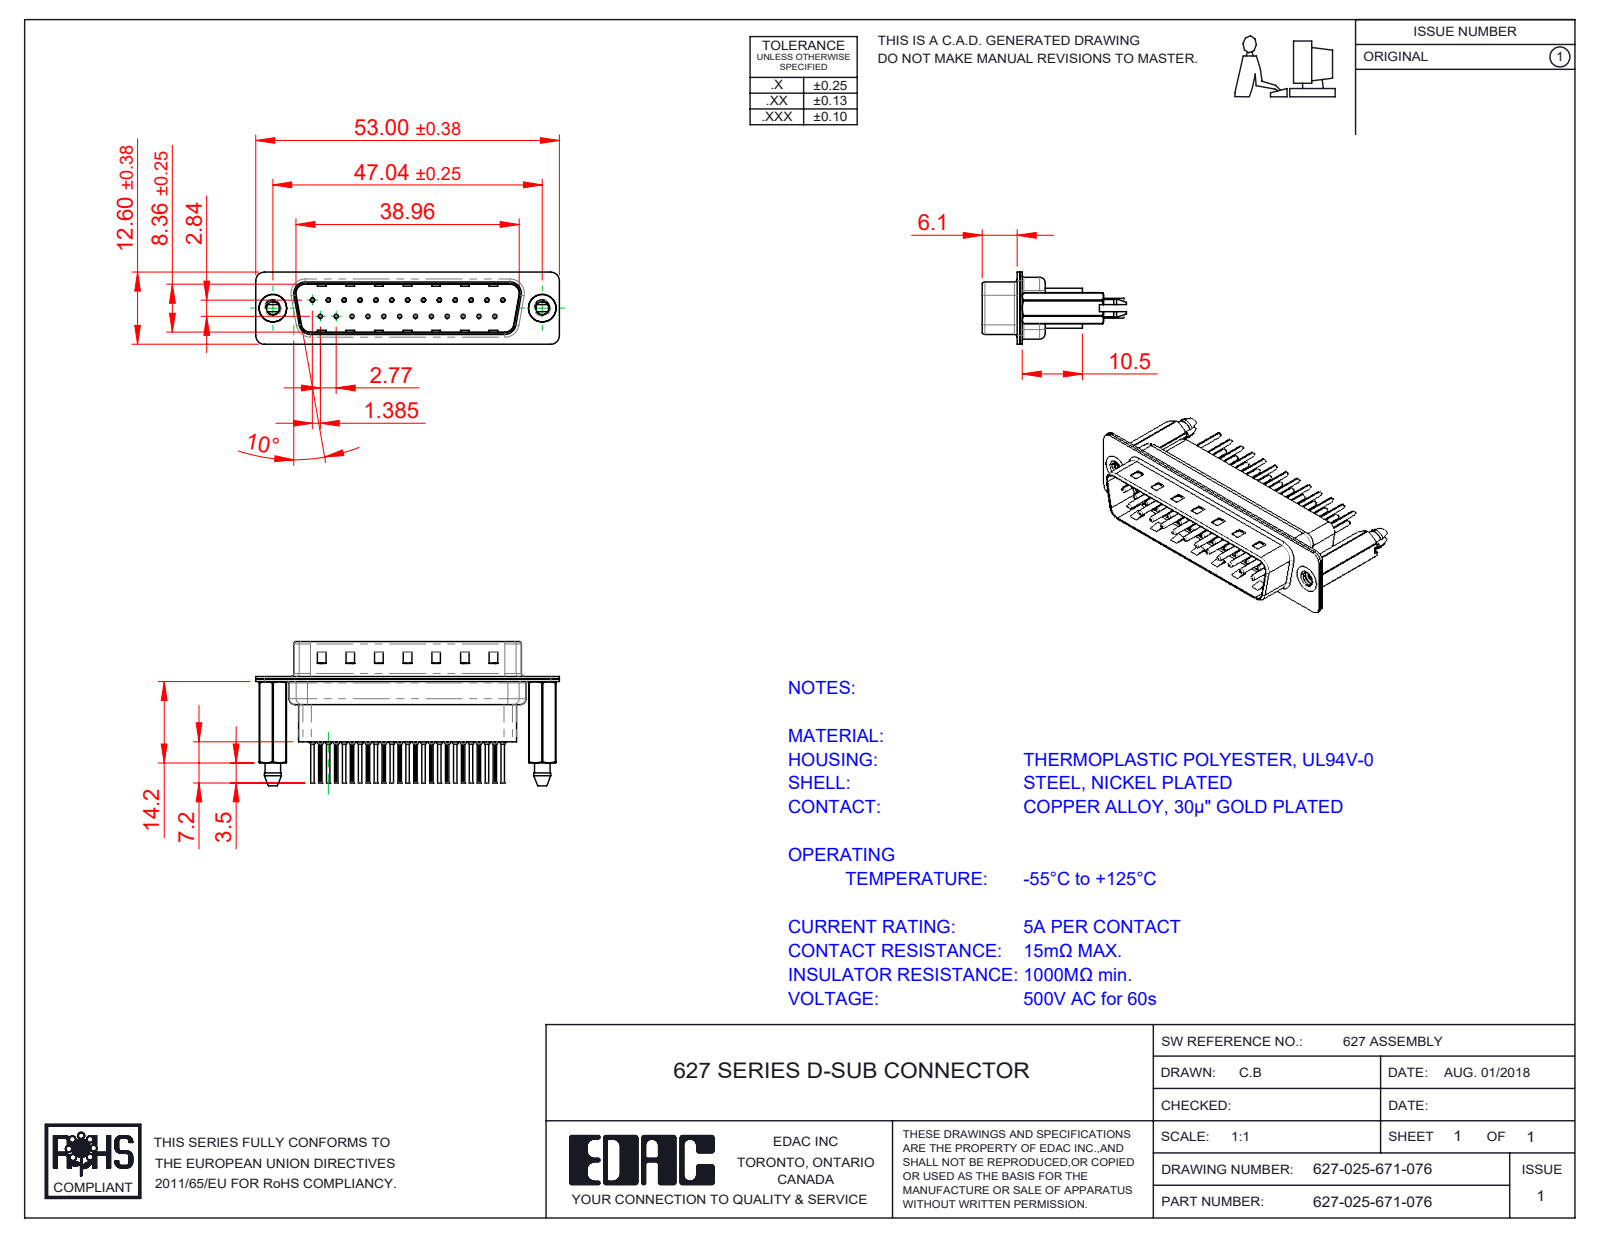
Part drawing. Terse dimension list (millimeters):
name: 627 Housing_25 HP; 627 Contact Row 1_61; 627 Shell Front_25 Contacts; 627-025-671-076 (+3 more)
written by: SolidWorks 2020 (CONFIG_CONTROL_DESIGN)
unit: mm
bodies: 30 solids, 2934 faces (803 planar, 1128 cylindrical, 1003 other)
size: 53 × 25.1 × 12.6
volume: 4 180 mm³; area: 10 793 mm²
holes: 25× ⌀0.2, 25× ⌀0.35, 25× ⌀1.1, 25× ⌀1.6, 2× ⌀2.26, 2× ⌀4, 2× ⌀4.8
bosses: 25× ⌀2, 25× ⌀1.5, 25× ⌀0.75, 25× ⌀0.6, 2× ⌀4.9
rounds: 50× R0.1, 18× R1.5, 12× R2, 10× R1.6, 8× R0.5, 4× R0.25, 4× R0.6, 4× R0.65
face distances: 0.4, 0.45, 0.82, 9.58, 0.68, 7.68, 1.5, 0.9, 1.08, 8.08
hole spacings: 3.16, 8.31, 2.77, 5.54, 11.08, 16.62, 5.03, 5.04
